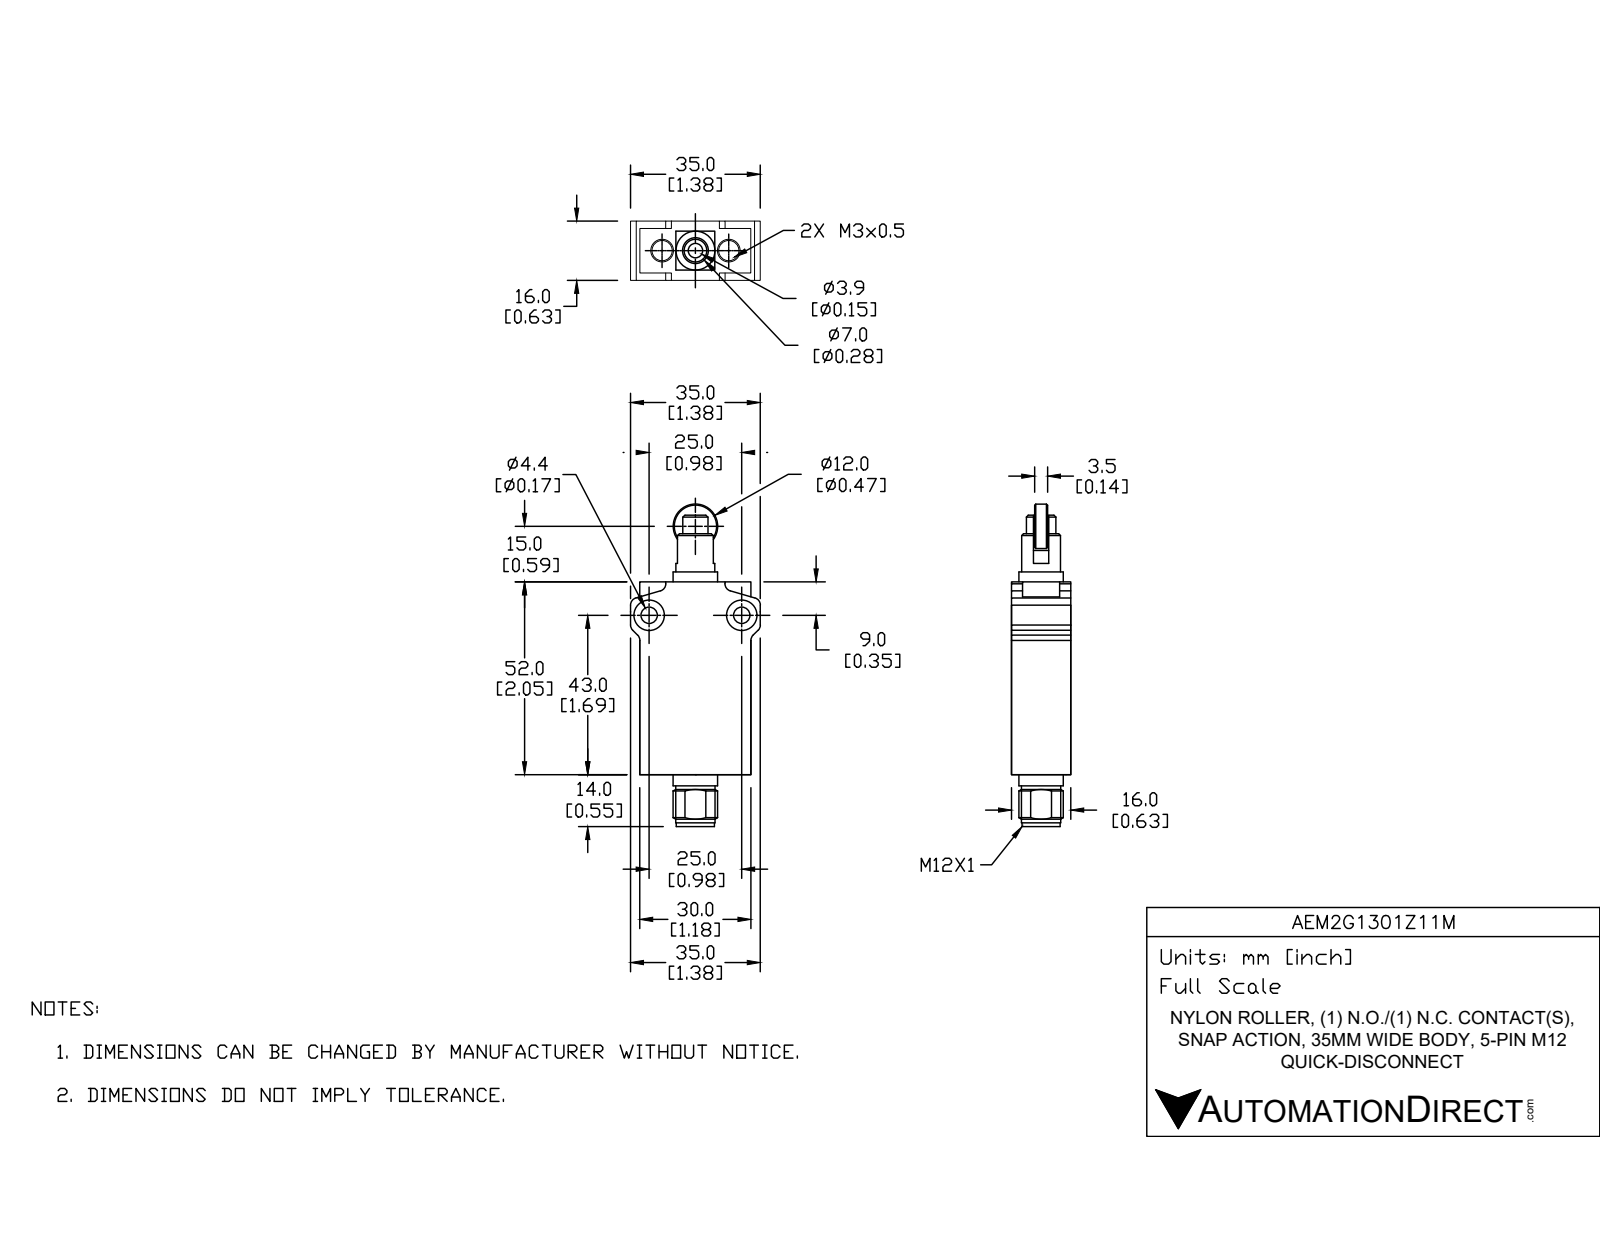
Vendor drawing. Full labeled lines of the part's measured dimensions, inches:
Part name (STEP PRODUCT): AEM2G1301Z11M
STEP written by: SolidWorks 2017 (AUTOMOTIVE_DESIGN)
Units: inches
Bodies: 4 solids, 180 faces (67 planar, 72 cylindrical, 41 other)
Overall size (bounding box): 3.425 × 1.378 × 0.63
Volume: 1.643 in³ · Surface area: 14.59 in²
Round holes (diameter × count): ⌀0.118 ×2, ⌀0.173 ×2, ⌀0.323 ×2, ⌀0.317 ×1
Round bosses / shafts (diameter × count): ⌀0.472 ×2, ⌀0.417 ×1, ⌀0.413 ×1, ⌀0.406 ×1, ⌀0.313 ×1, ⌀0.22 ×1
Partial cylindrical surfaces — rounded edges, fillets, slot ends (radius × count): R0.079 ×8, R0.256 ×1
Main face-to-face distances: 0.63, 1.181, 2.047, 0.472, 1.858, 0.189, 0.234, 0.15, 0.157, 0.238
Hole centre spacings: 0.374, 0.748, 0.984
